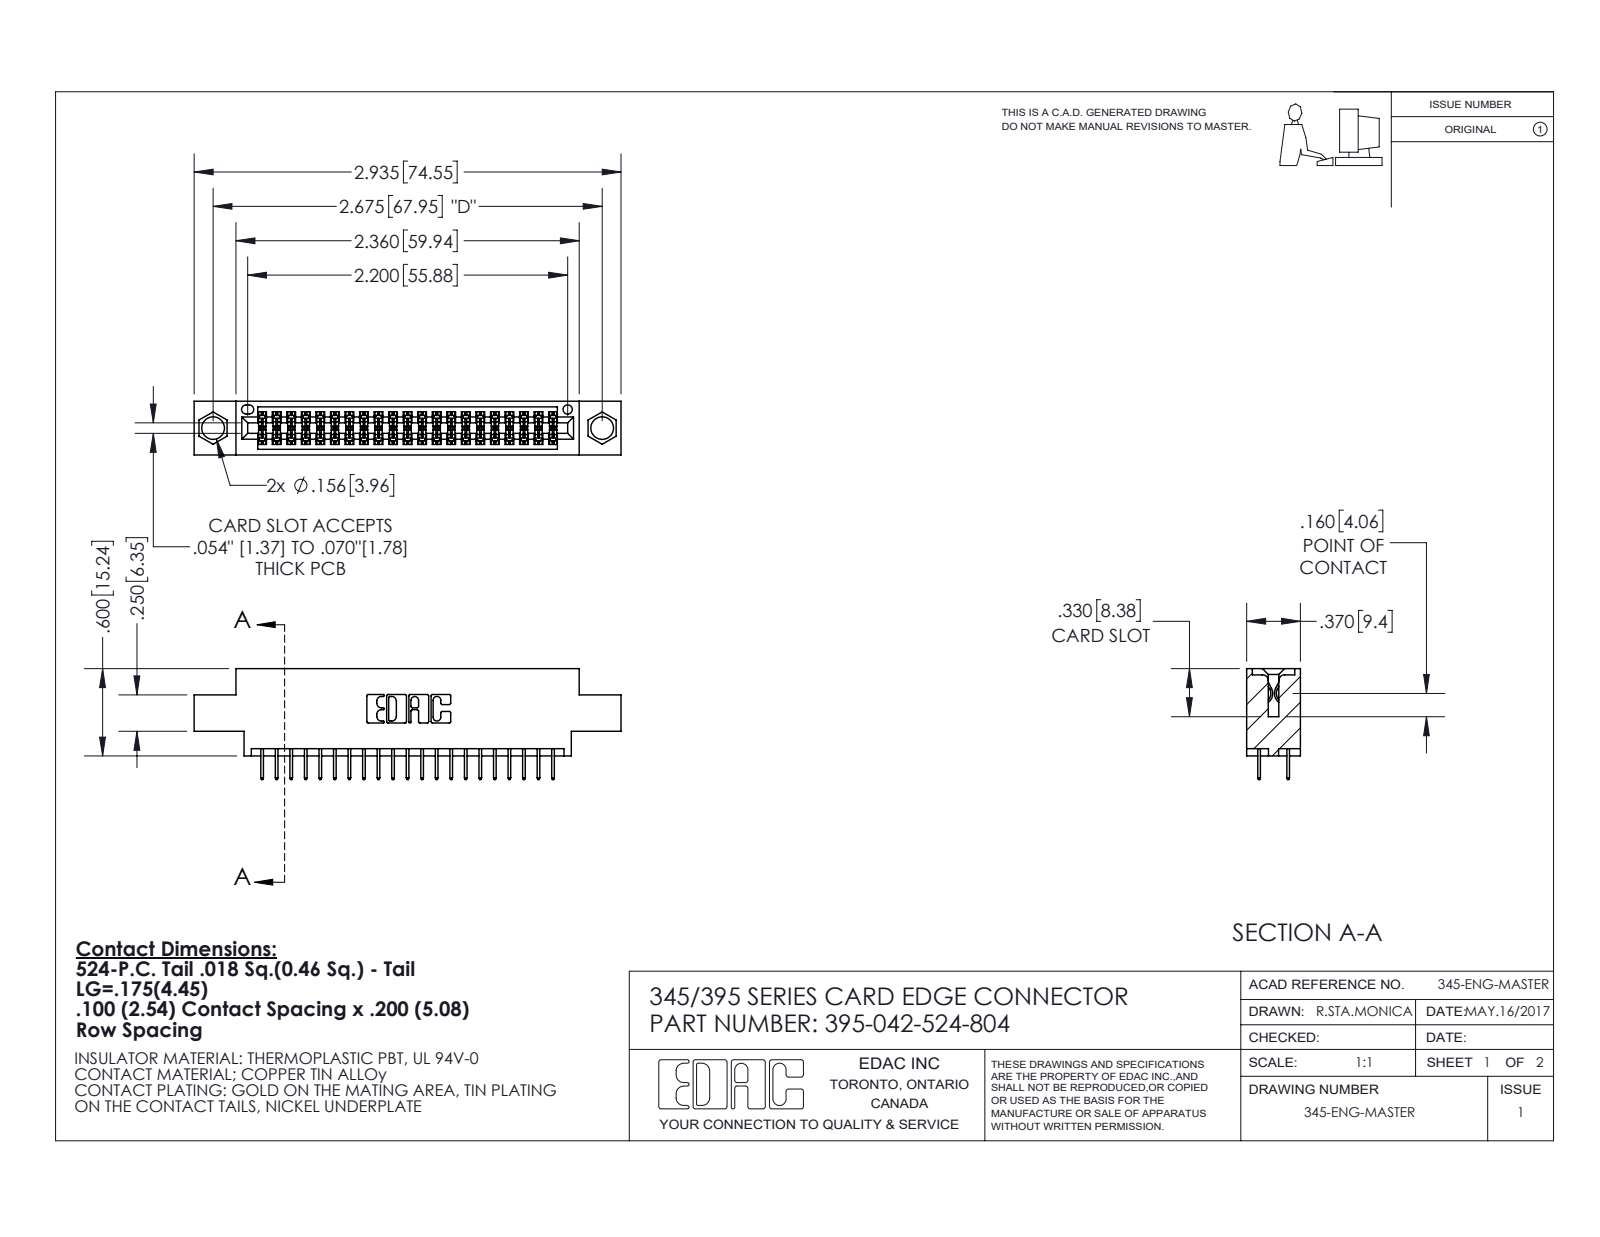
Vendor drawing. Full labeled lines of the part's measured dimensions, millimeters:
Part name (STEP PRODUCT): 395-042-524-804; 345 Part_0.170 Offset - 0.156 Dia-TI; 345-292-001_345-293-124
STEP written by: SolidWorks 2020 (CONFIG_CONTROL_DESIGN)
Units: millimetres
Bodies: 43 solids, 2412 faces (1736 planar, 676 cylindrical, 0 other)
Overall size (bounding box): 74.5 × 19.4 × 9.4
Volume: 6 770 mm³ · Surface area: 9 419 mm²
Round holes (diameter × count): ⌀4 ×2, ⌀1.6 ×1
Partial cylindrical surfaces — rounded edges, fillets, slot ends (radius × count): R0.2 ×84, R0.3 ×22, R0.2 ×6, R0.8 ×6, R0.7 ×3, R0.4 ×2, R0.5 ×2, R0.6 ×2
Main face-to-face distances: 1.8, 7.6, 9.4, 5.1, 2.5, 6.9, 0.6, 5.7, 4.4, 1.8
Hole centre spacings: 6.9, 62, 67.9
